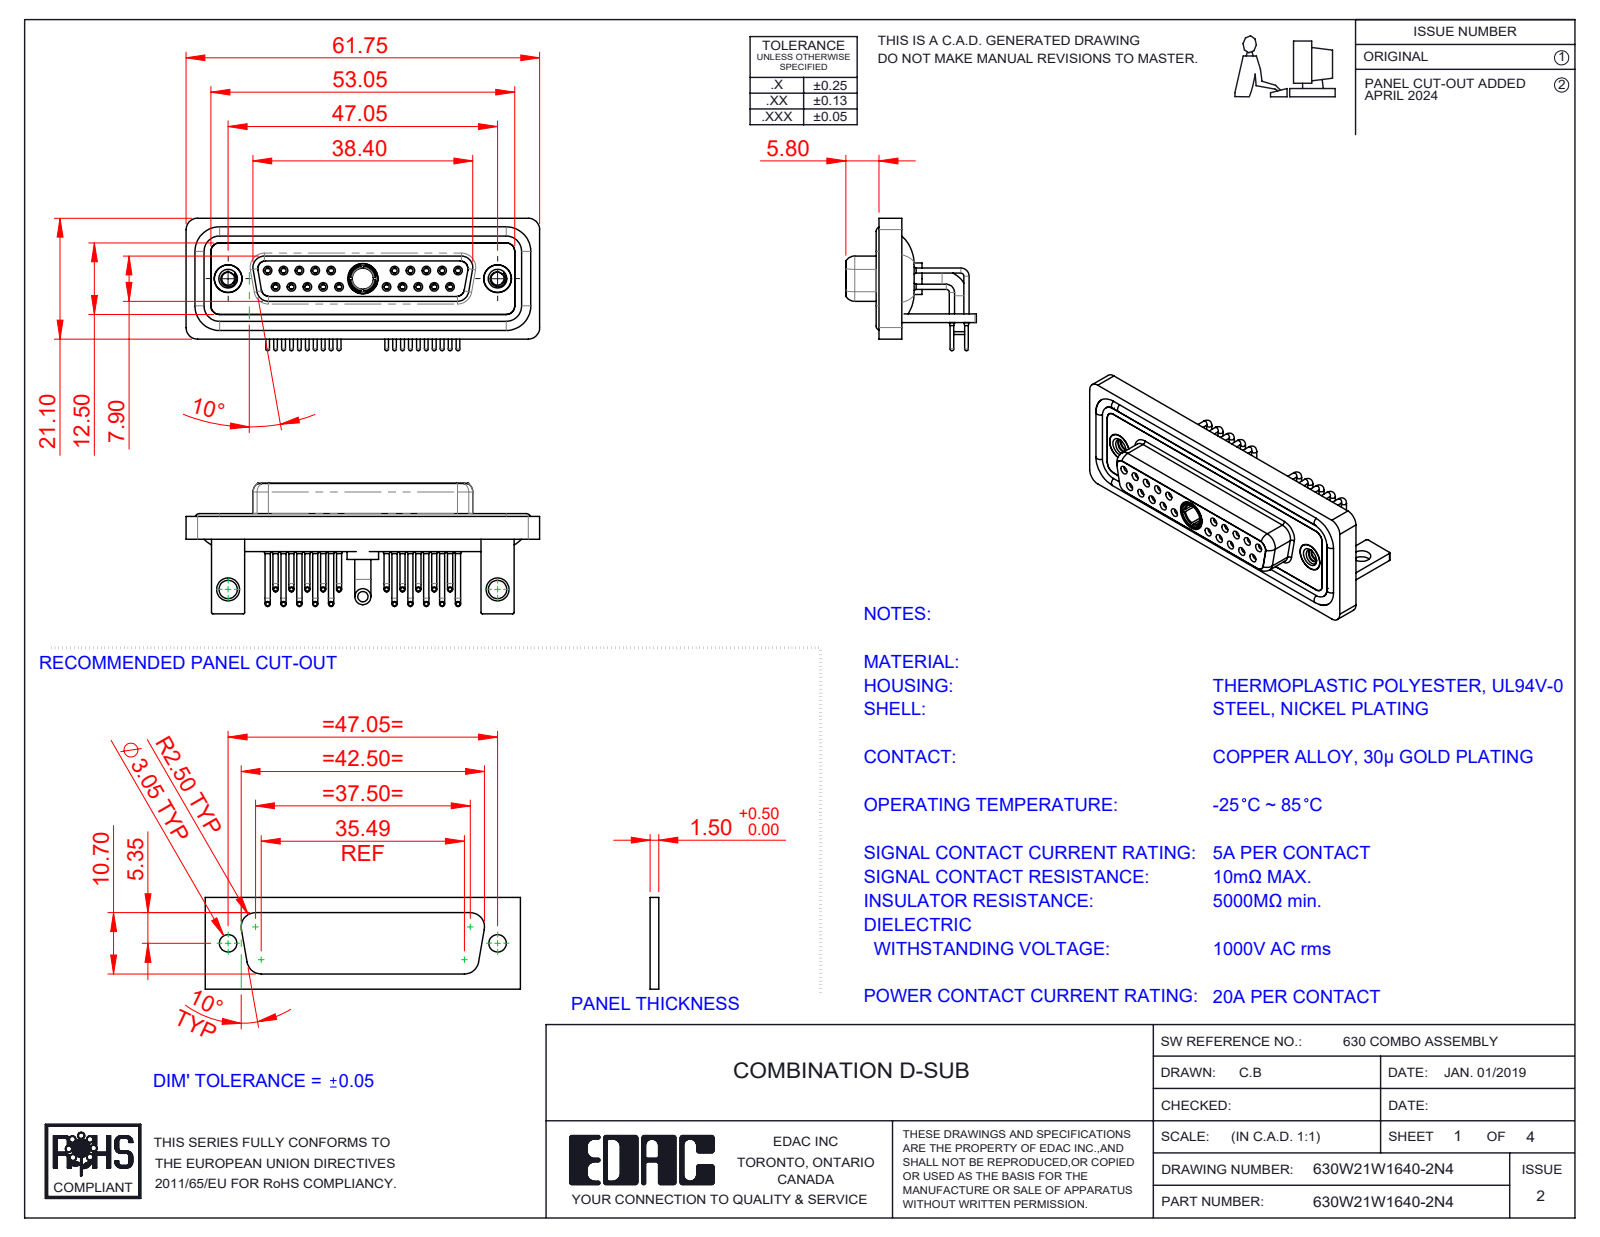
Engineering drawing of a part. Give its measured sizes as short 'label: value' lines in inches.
name: 630Combo Housing_21W1; 630Combo Contact Row 1_50 Contacts; 630Combo Shell Rear_25 Contacts; 630Combo Waterproof Housing_25 Contacts (+6 more)
written by: SolidWorks 2023 (CONFIG_CONTROL_DESIGN)
unit: in
bodies: 31 solids, 1572 faces (454 planar, 697 cylindrical, 421 other)
size: 2.431 × 0.91 × 0.898
volume: 0.541 in³; area: 24.05 in²
holes: 20× ⌀0.035, 20× ⌀0.043, 20× ⌀0.059, 20× ⌀0.079, 10× ⌀0.063, 10× ⌀0.067, 3× ⌀0.191, 2× ⌀0.089, 2× ⌀0.126, 2× ⌀0.157, 2× ⌀0.159, 2× ⌀0.197
bosses: 20× ⌀0.035, 20× ⌀0.026, 14× ⌀0.063, 2× ⌀0.195, 2× ⌀0.189, 2× ⌀0.11, 1× ⌀0.217, 1× ⌀0.205
rounds: 19× R0.079, 18× R0.059, 16× R0.01, 8× R0.053, 8× R0.063, 5× R0.02, 4× R0.024, 4× R0.026
face distances: 0.016, 0.071, 0.114, 0.146, 0.059, 0.161, 0.043, 0.055, 0.063, 0.098
hole spacings: 0.124, 0.109, 0.218, 0.327, 0.198, 0.763, 0.826, 0.872
